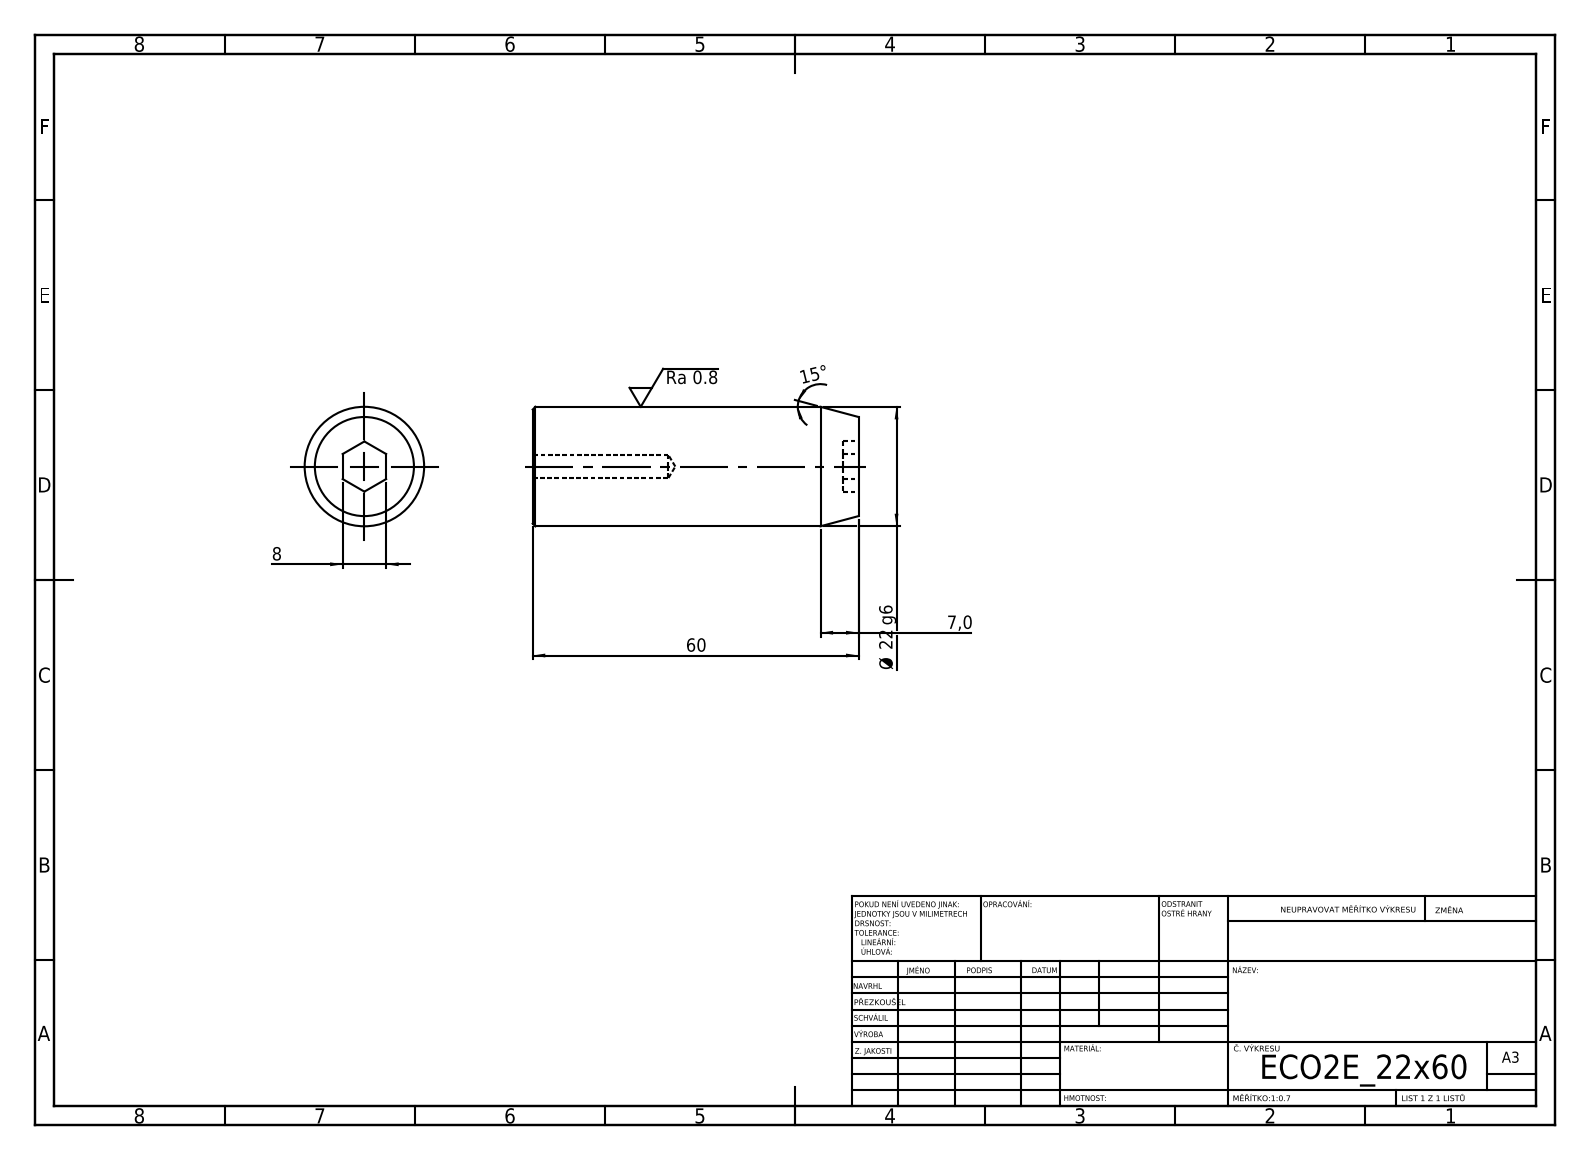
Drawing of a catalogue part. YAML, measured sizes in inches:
step_written_by: "SolidWorks 2019 (CONFIG_CONTROL_DESIGN)"
units: inches
bodies: {solids: 1, faces: 19, planar: 9, cylindrical: 4, other: 6}
overall_size: [2.362, 0.866, 0.866]
volume: 1.334
surface_area: 7.986
round_holes:
  - {diameter: 0.165, count: 1}
round_bosses_or_shafts:
  - {diameter: 0.866, count: 1}
face_to_face_distances: [2.362, 0.11, 2.252, 0.315]
